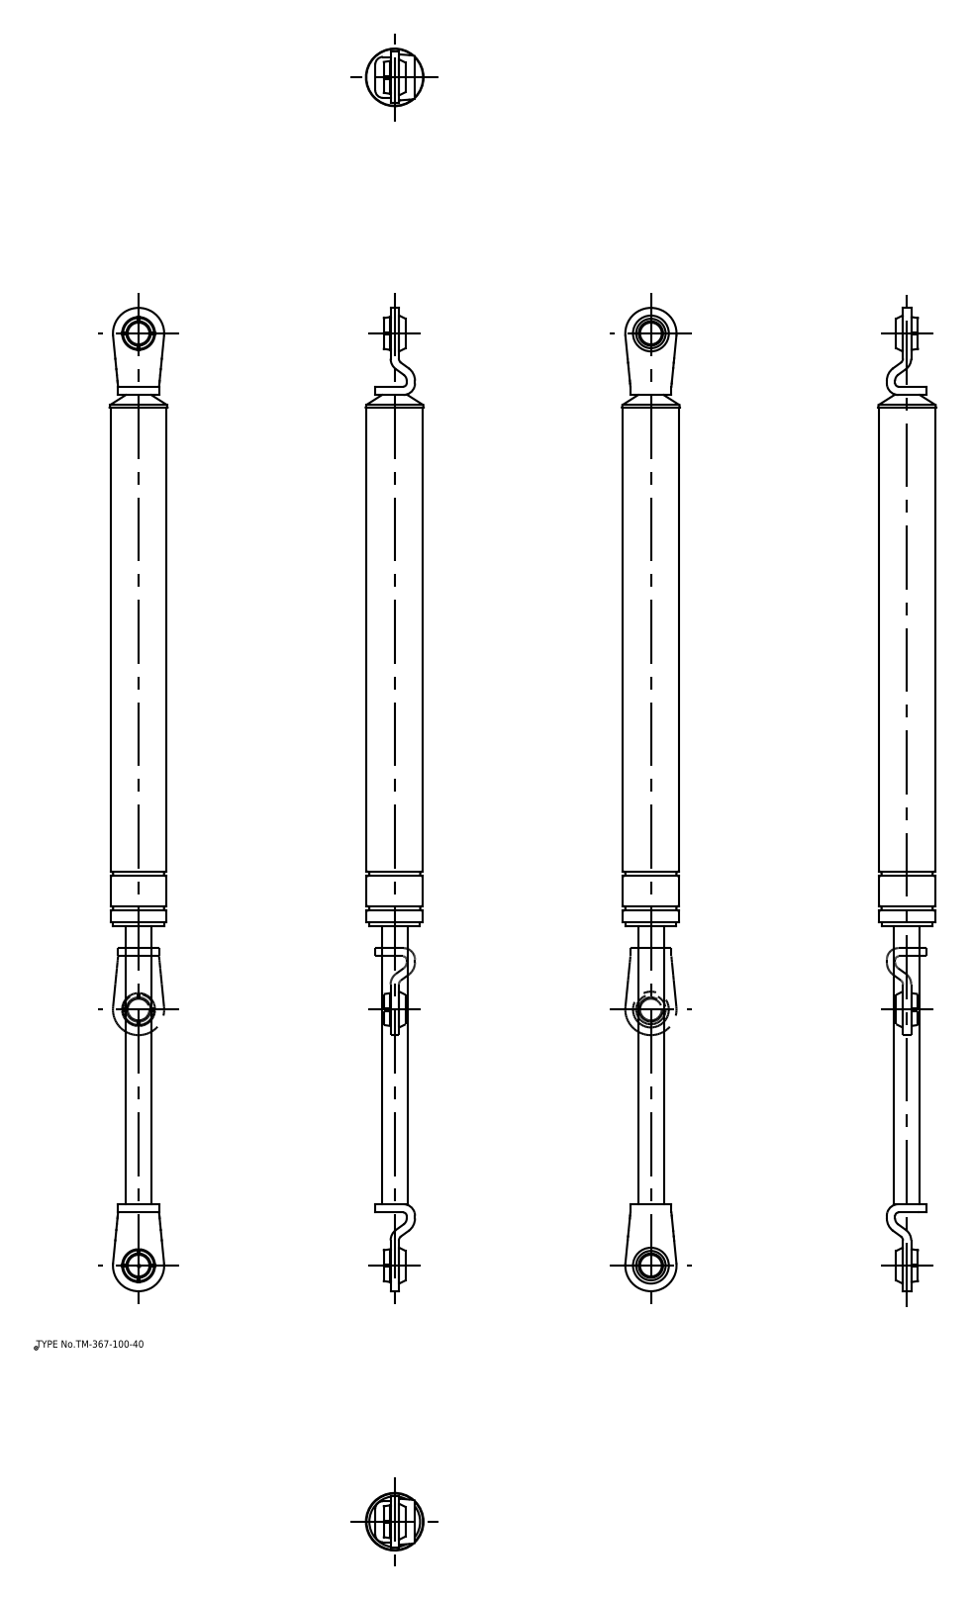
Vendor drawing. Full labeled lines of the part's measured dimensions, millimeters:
Part name (STEP PRODUCT): TM_367_100_40; TM_367_100_40_div
STEP written by: spGate 16.7.1 (AUTOMOTIVE_DESIGN)
Units: millimetres
Bodies: 2 solids, 153 faces (79 planar, 40 cylindrical, 34 other)
Overall size (bounding box): 384 × 22.5 × 22.5
Volume: 91 812 mm³ · Surface area: 23 072 mm²
Round holes (diameter × count): ⌀8.5 ×2
Round bosses / shafts (diameter × count): ⌀12.1 ×2, ⌀22 ×1, ⌀19.8 ×1, ⌀10 ×1
Partial cylindrical surfaces — rounded edges, fillets, slot ends (radius × count): R3 ×4, R1.5 ×2, R2 ×2, R4.5 ×2, R5 ×2, R6 ×2, R10 ×2
Main face-to-face distances: 3.2, 319.2, 5.85, 3.35, 6, 210.7, 111.7, 322.4, 2.65, 3.19
Hole centre spacings: 364
